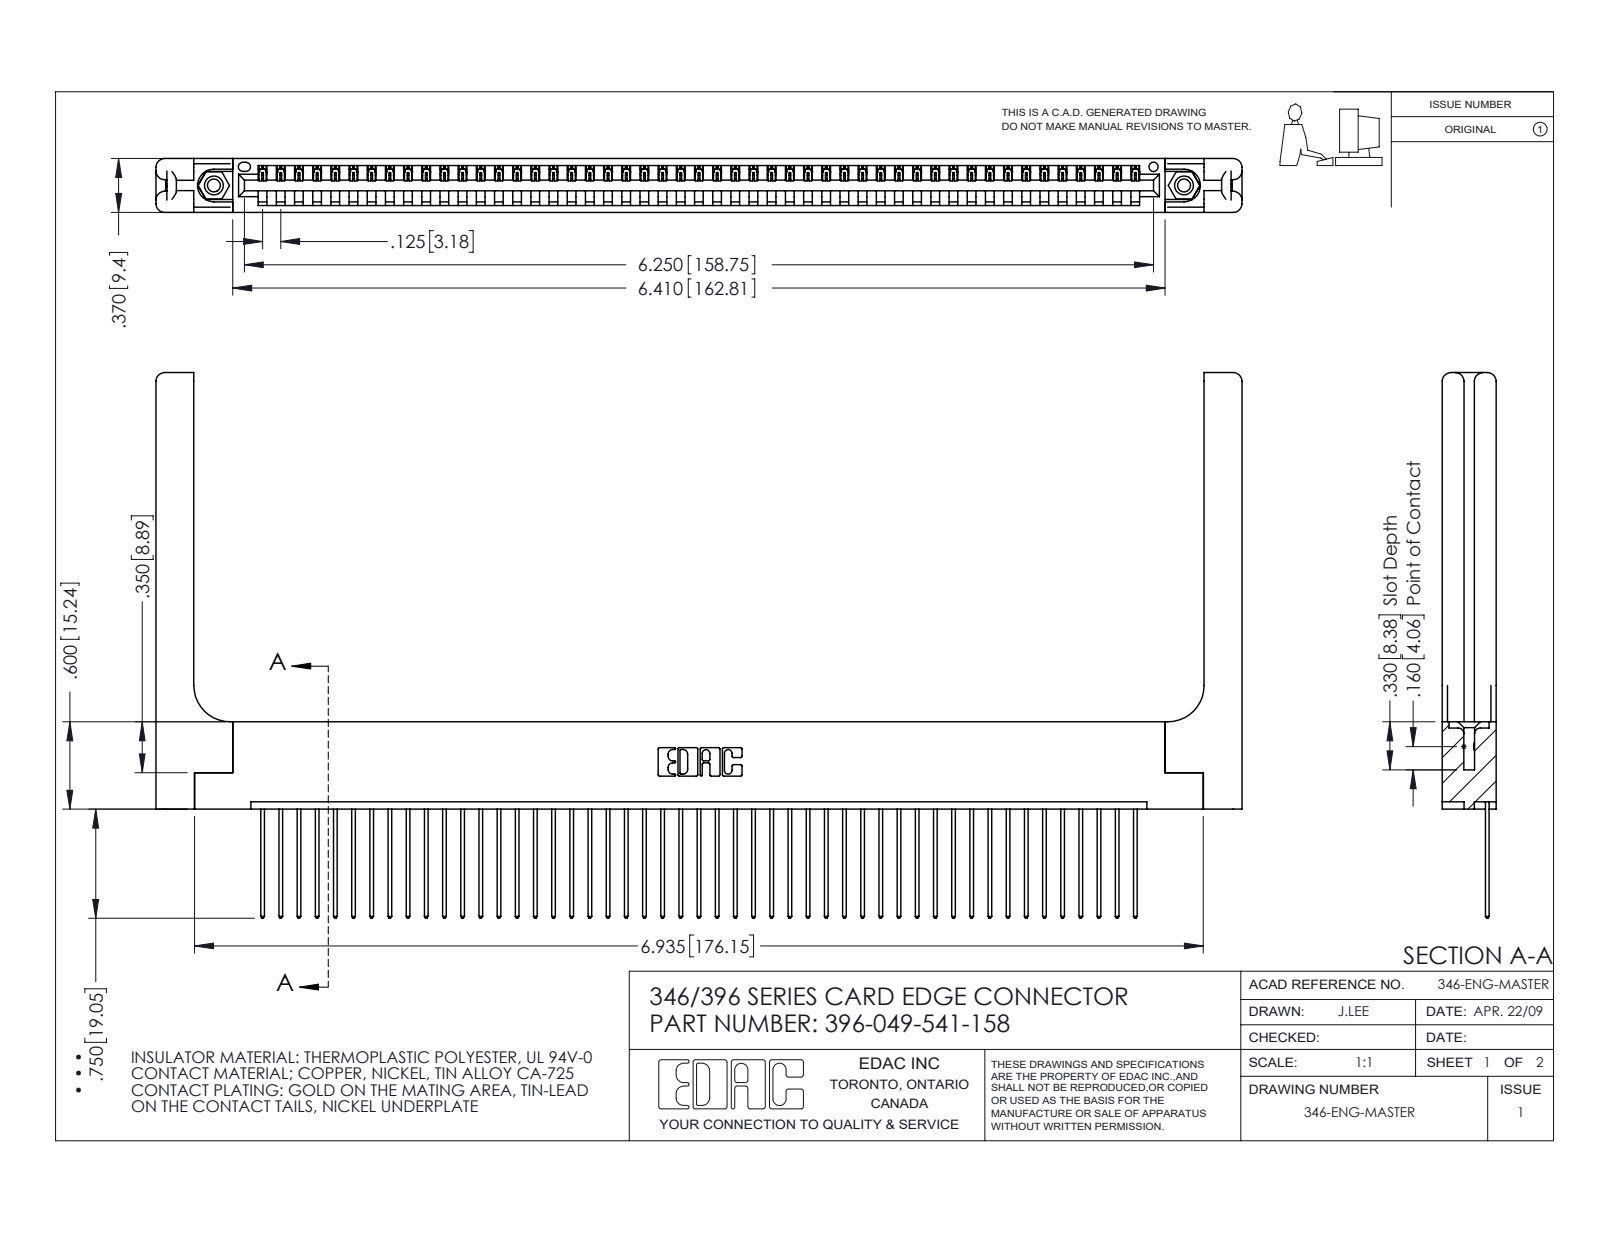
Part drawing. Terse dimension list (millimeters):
name: 346 Part_Flush Mounting Lugs - 0.156 Dia-TH; 345-250-001_345-250-001-102; 345-292-001_345-293-141; 346-220-058_345-220-058 (+1 more)
written by: SolidWorks 2016 (CONFIG_CONTROL_DESIGN)
unit: mm
bodies: 54 solids, 3220 faces (2184 planar, 976 cylindrical, 60 other)
size: 189.6 × 95.3 × 9.4
volume: 25 880 mm³; area: 29 160 mm²
holes: 2× ⌀2.3, 2× ⌀3.2, 2× ⌀4, 1× ⌀1.6
bosses: 2× ⌀3.9
rounds: 98× R0.2, 98× R0.3, 22× R0.3, 16× R1.5, 6× R0.2, 6× R0.8, 3× R0.7, 2× R0.8
face distances: 1.2, 8.2, 9.4, 1.8, 3.8, 7.6, 0.6, 6.4, 3.8, 5.6
hole spacings: 6.2, 164.1, 169.4
